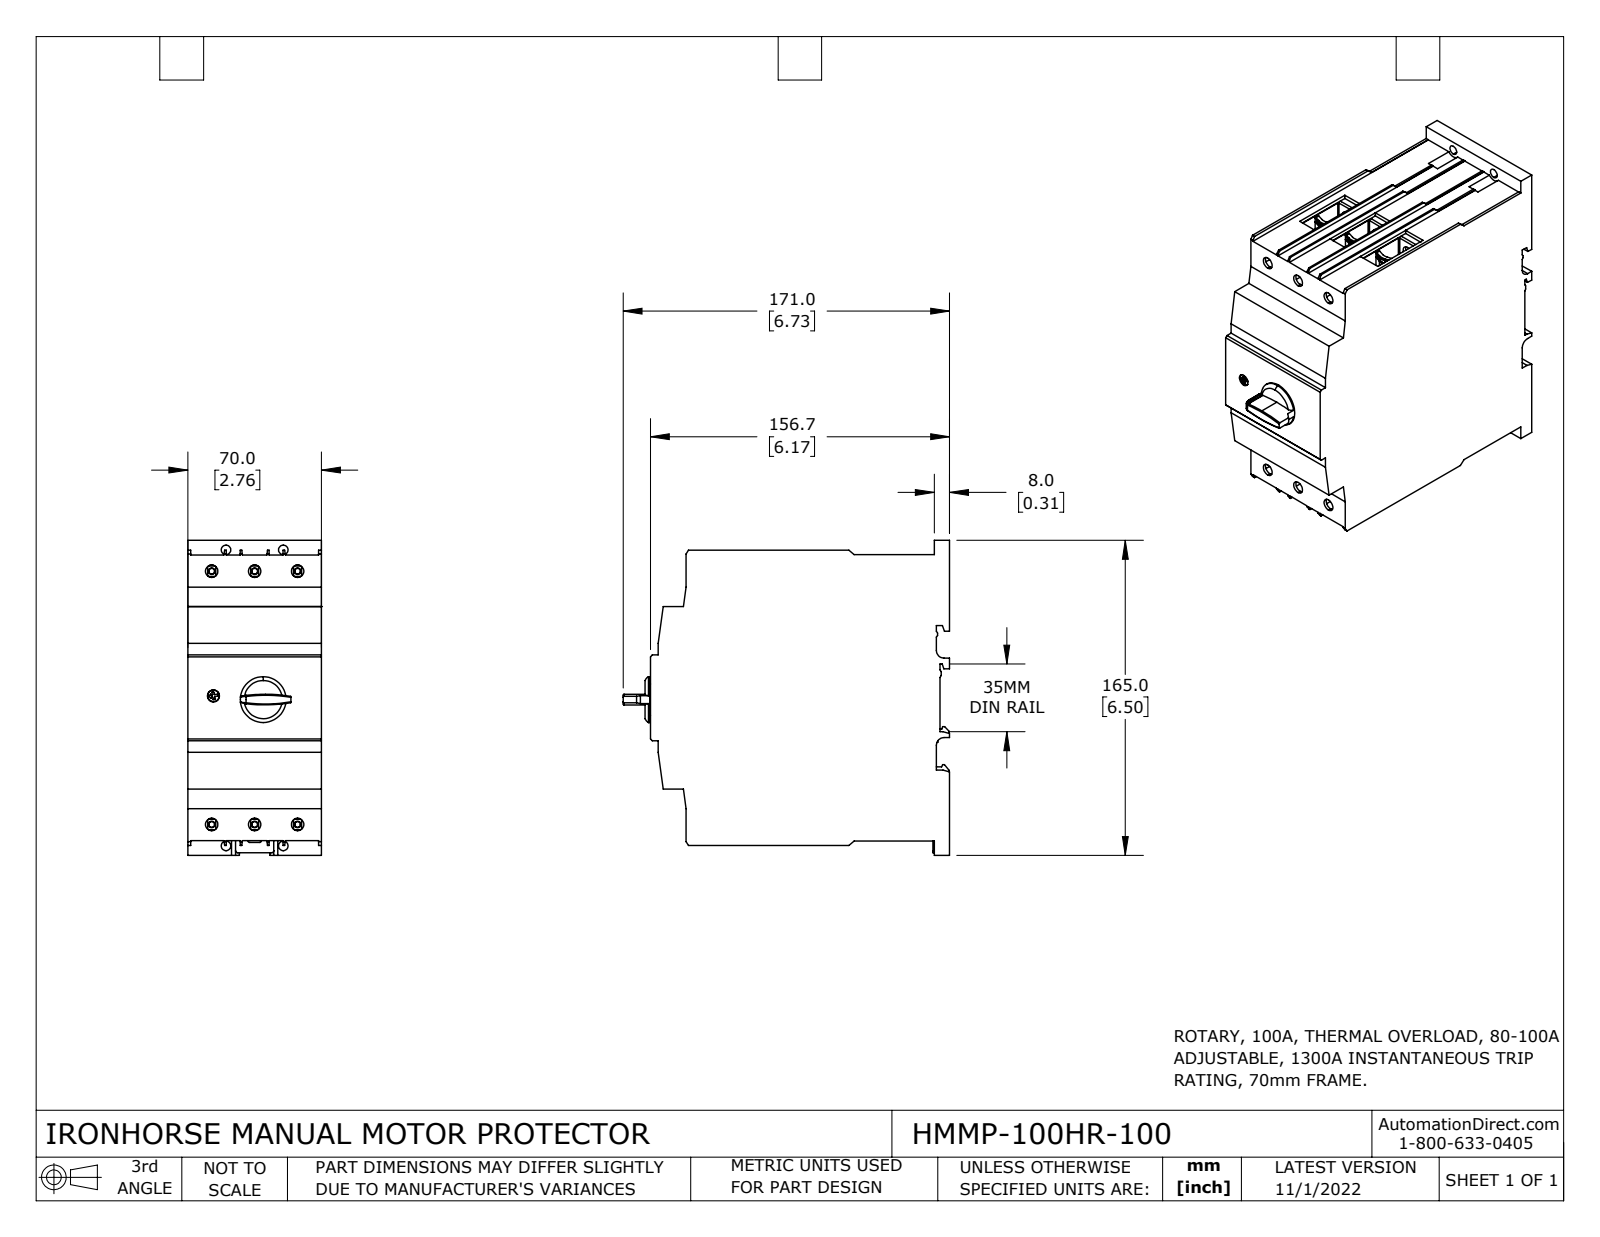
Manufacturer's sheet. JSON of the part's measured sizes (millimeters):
{"part_name": "HMMP-100HR-100", "step_written_by": "SolidWorks 2021 (CONFIG_CONTROL_DESIGN)", "units": "millimeters", "bodies": {"solids": 16, "faces": 1259, "planar": 753, "cylindrical": 399, "other": 107}, "overall_size": [171, 165, 70], "volume_mm3": 1431000, "surface_area_mm2": 149900, "round_holes": [[3, 8], [4, 6], [6.5, 6], [5, 4], [6.3, 1]], "round_bosses_or_shafts": [[24, 1], [16.4, 1], [6, 1]], "partial_cylinders_radius": [[0.3, 96], [1, 40], [0.5, 23], [2.3, 14], [0.2, 12], [4.3, 4], [5, 4], [80, 4]], "face_to_face_distances": [70, 22.5, 16, 1.8, 27, 45, 4.5, 43, 132.6, 65.5], "hole_center_spacings": [13.48, 18.72, 22.5, 39.14, 134.5, 144, 144.58, 148.61]}
